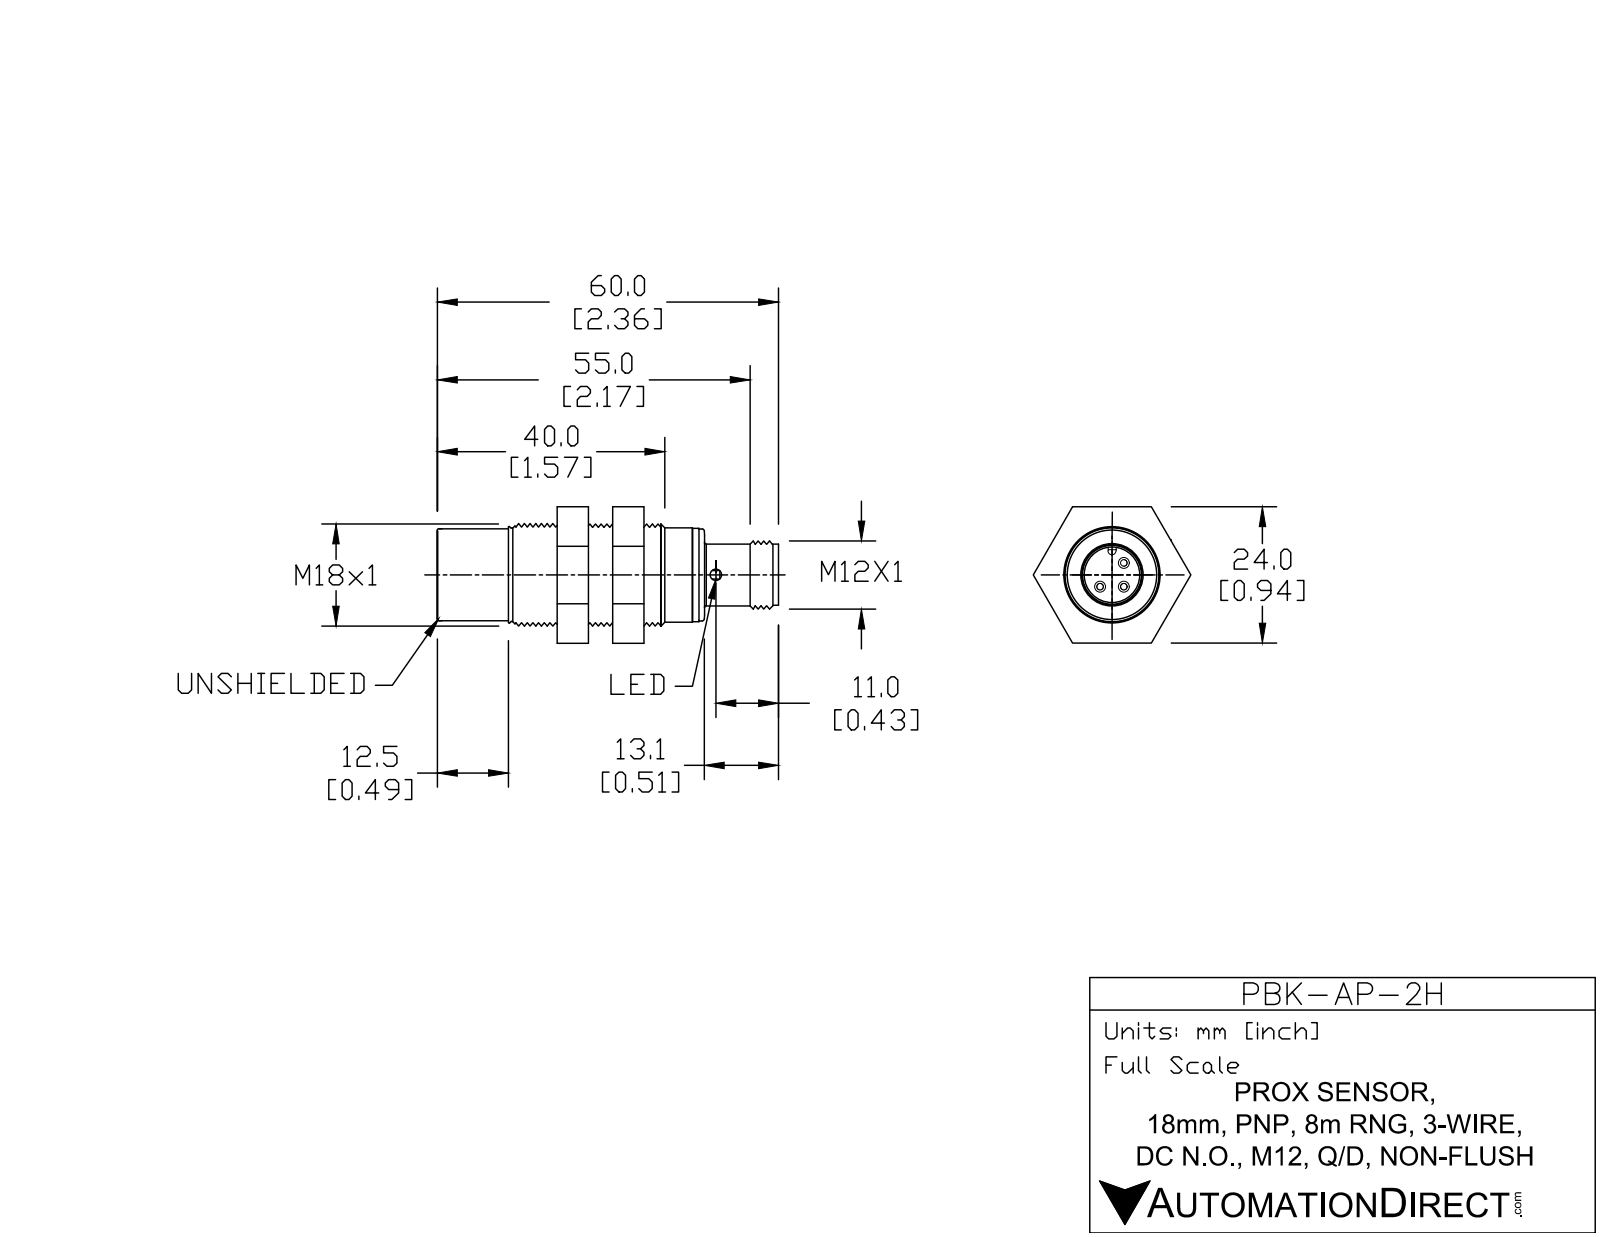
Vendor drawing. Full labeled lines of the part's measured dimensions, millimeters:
Part name (STEP PRODUCT): PBK-AP-2H
STEP written by: SolidWorks 2011 (AUTOMOTIVE_DESIGN)
Units: millimetres
Bodies: 8 solids, 66 faces (38 planar, 18 cylindrical, 10 other)
Overall size (bounding box): 60 × 27.69 × 24.57
Volume: 14 150 mm³ · Surface area: 6 935 mm²
Round holes (diameter × count): ⌀1.25 ×1, ⌀8.5 ×1, ⌀10.5 ×1, ⌀17 ×1
Round bosses / shafts (diameter × count): ⌀1 ×3, ⌀18 ×1, ⌀16.8 ×1, ⌀16.6 ×1, ⌀16.15 ×1, ⌀16 ×1, ⌀12 ×1, ⌀10.9 ×1
Main face-to-face distances: 4.5, 10, 24, 27.75, 32.25, 9.75, 15.25, 5.25, 14.5, 19.75
